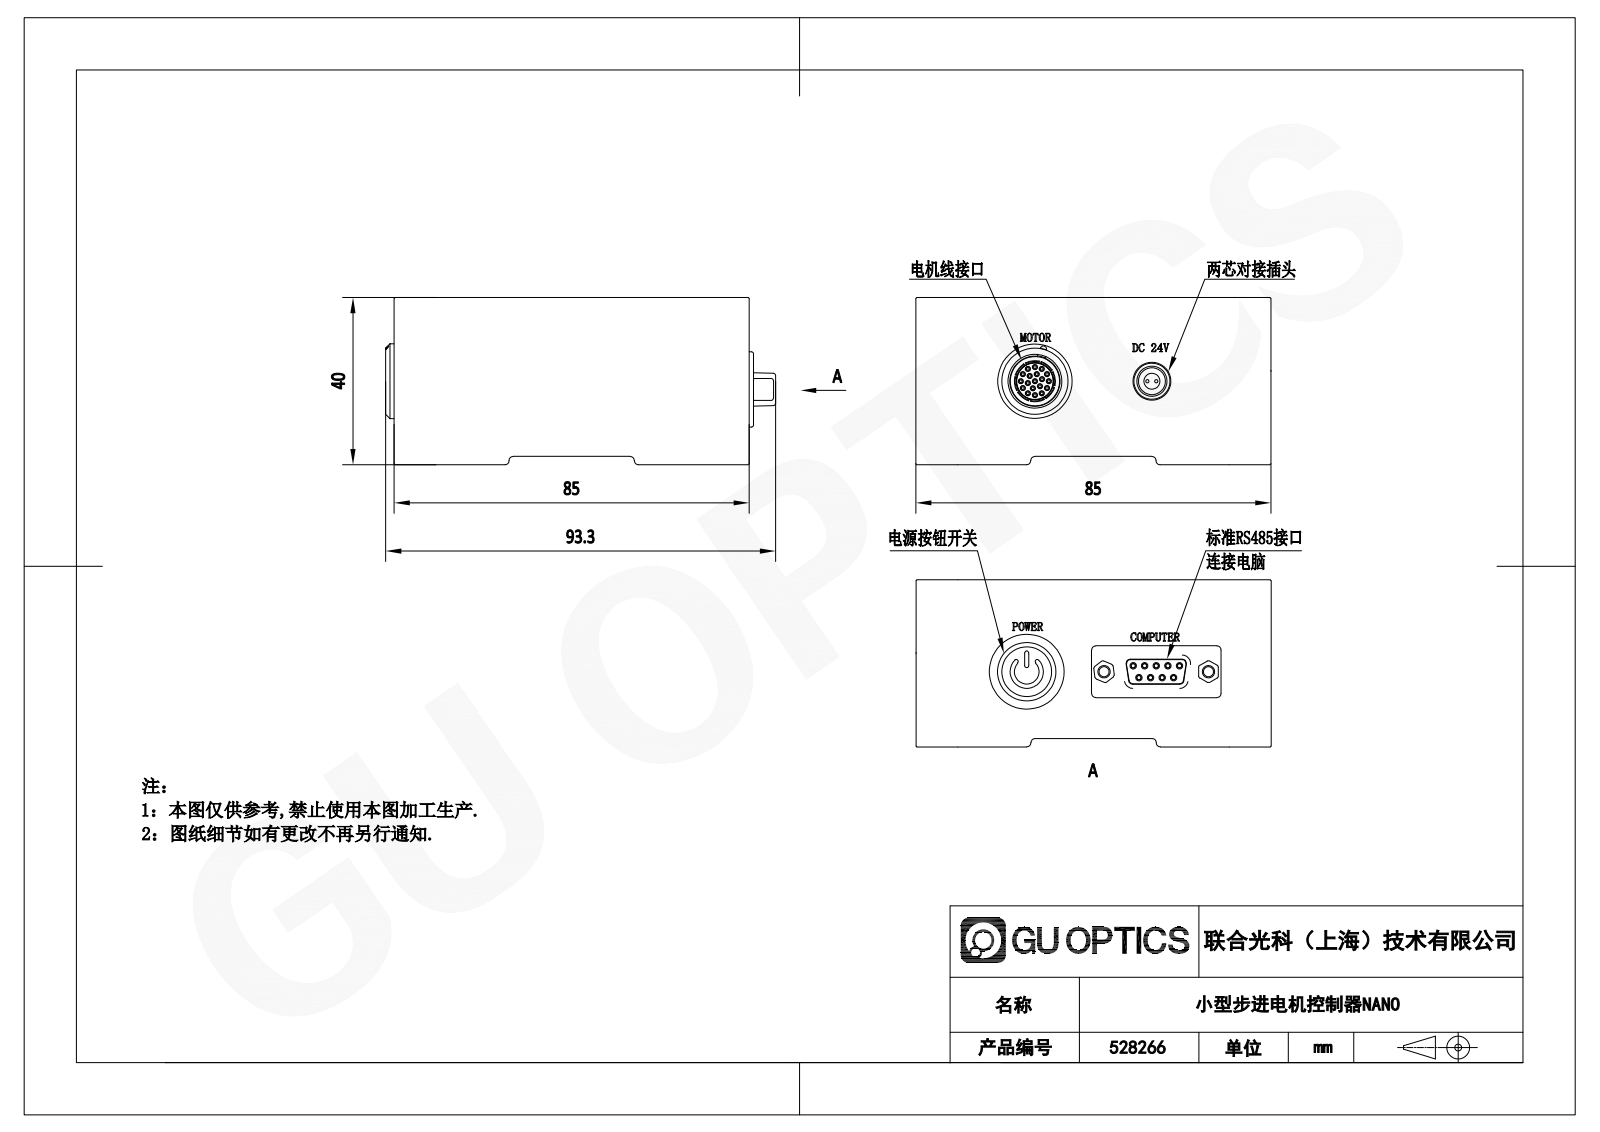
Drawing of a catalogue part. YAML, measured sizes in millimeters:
part_name: "528280"
step_written_by: "SolidWorks 2020 (CONFIG_CONTROL_DESIGN)"
units: millimeters
bodies: {solids: 14, faces: 1296, planar: 642, cylindrical: 332, other: 322}
overall_size: [93.3, 85, 40]
volume: 132910
surface_area: 67068
round_holes:
  - {diameter: 0.7, count: 19}
  - {diameter: 1.3, count: 19}
  - {diameter: 2.05, count: 12}
  - {diameter: 1, count: 9}
  - {diameter: 1.1, count: 9}
  - {diameter: 2.9, count: 8}
  - {diameter: 0.9, count: 2}
  - {diameter: 2.5, count: 2}
  - {diameter: 3.2, count: 2}
  - {diameter: 6, count: 1}
  - {diameter: 9.1, count: 1}
  - {diameter: 10, count: 1}
round_bosses_or_shafts:
  - {diameter: 1.5, count: 9}
  - {diameter: 4.4, count: 4}
  - {diameter: 2.5, count: 4}
  - {diameter: 3, count: 2}
  - {diameter: 18, count: 1}
  - {diameter: 16, count: 1}
  - {diameter: 12, count: 1}
  - {diameter: 8.8, count: 1}
partial_cylinders:
  - {radius: 0.5, count: 44}
  - {radius: 0.3, count: 24}
  - {radius: 1, count: 24}
  - {radius: 0.2, count: 16}
  - {radius: 2, count: 16}
  - {radius: 1.45, count: 6}
  - {radius: 0.1, count: 4}
  - {radius: 0.92, count: 4}
face_to_face_distances: [5, 2, 36, 38, 3, 80, 33, 35, 85, 75]
hole_center_spacings: [3.35, 6.47, 2.9, 3.78, 4.49, 2.03, 5.8, 1.73]
